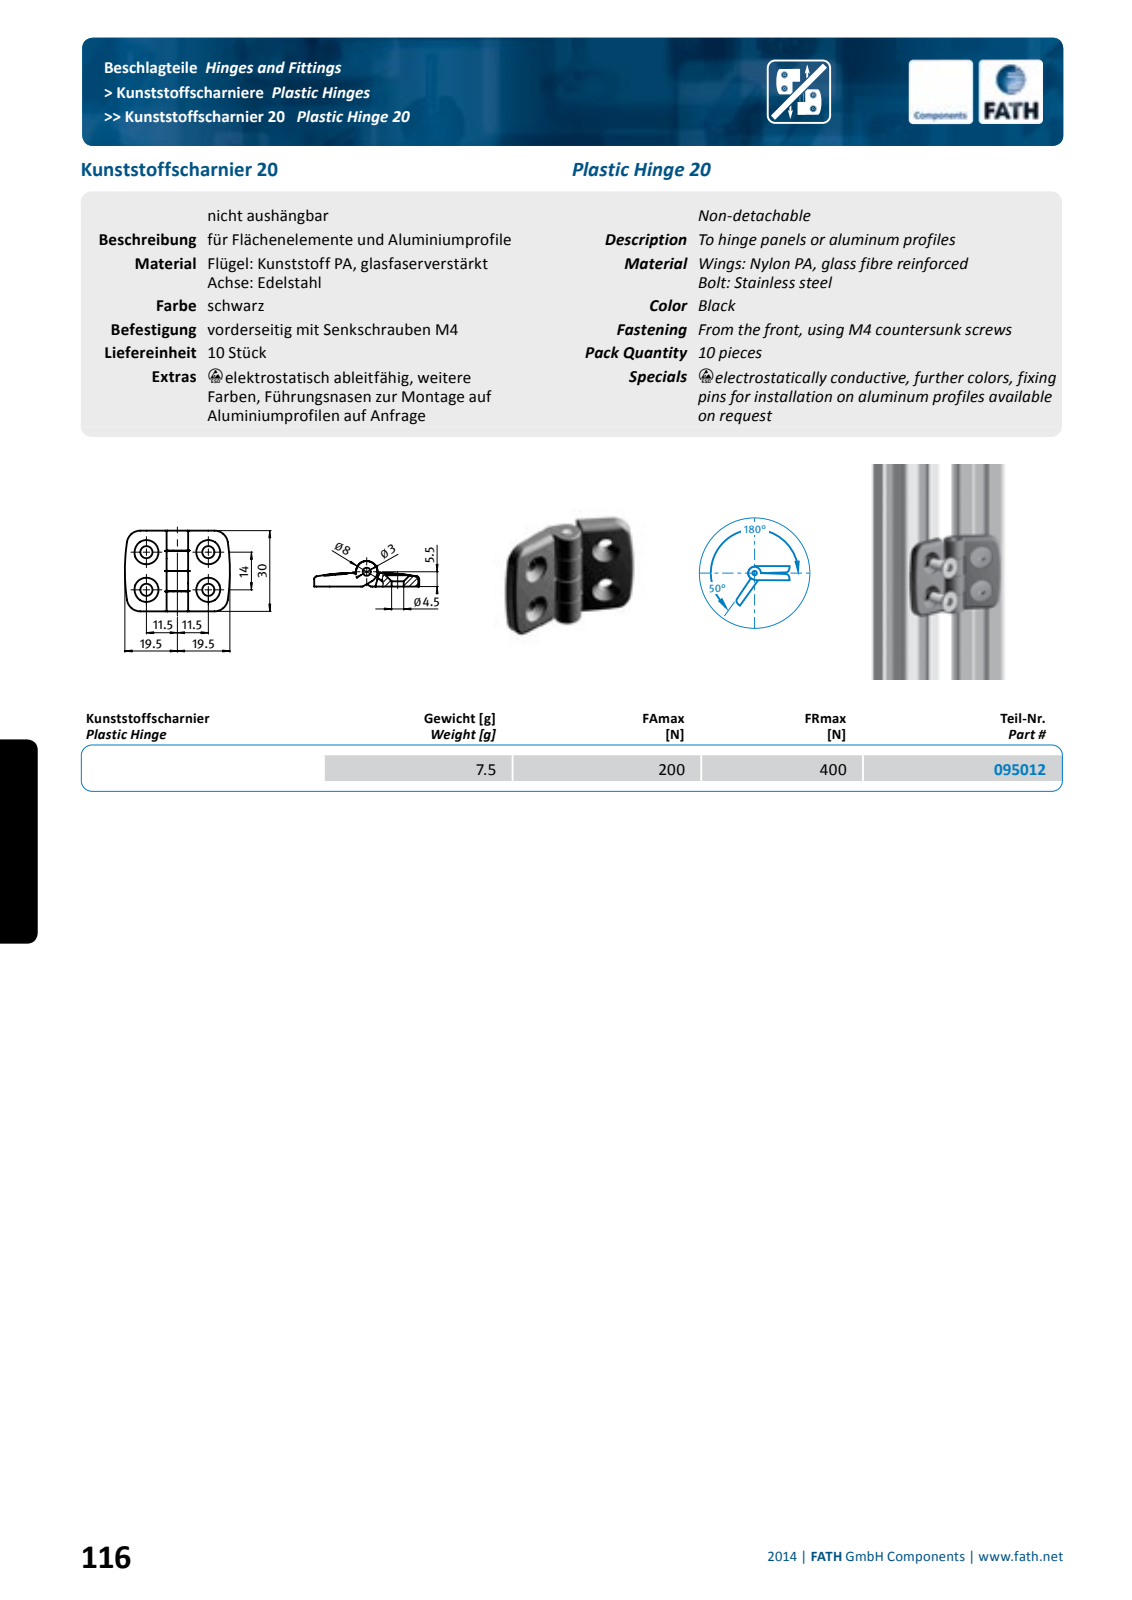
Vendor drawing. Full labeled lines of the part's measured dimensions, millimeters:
Part name (STEP PRODUCT): fath_095012_1; fath_095012_2; fath_095012_3
STEP written by: Spatial InterOp 3D (automotive_design)
Units: millimetres
Bodies: 3 solids, 174 faces (36 planar, 58 cylindrical, 80 other)
Overall size (bounding box): 39 × 30 × 9.5
Volume: 4 985 mm³ · Surface area: 4 146 mm²
Round holes (diameter × count): ⌀4.5 ×4, ⌀3 ×1
Round bosses / shafts (diameter × count): ⌀8 ×1
Partial cylindrical surfaces — rounded edges, fillets, slot ends (radius × count): R0.3 ×16, R4.5 ×4, R5 ×4, R75 ×2
Main face-to-face distances: 15, 7.4, 7.6, 1, 30, 22.4, 22.6, 12.2, 17.8, 4.8
Hole centre spacings: 14, 23, 26.93
